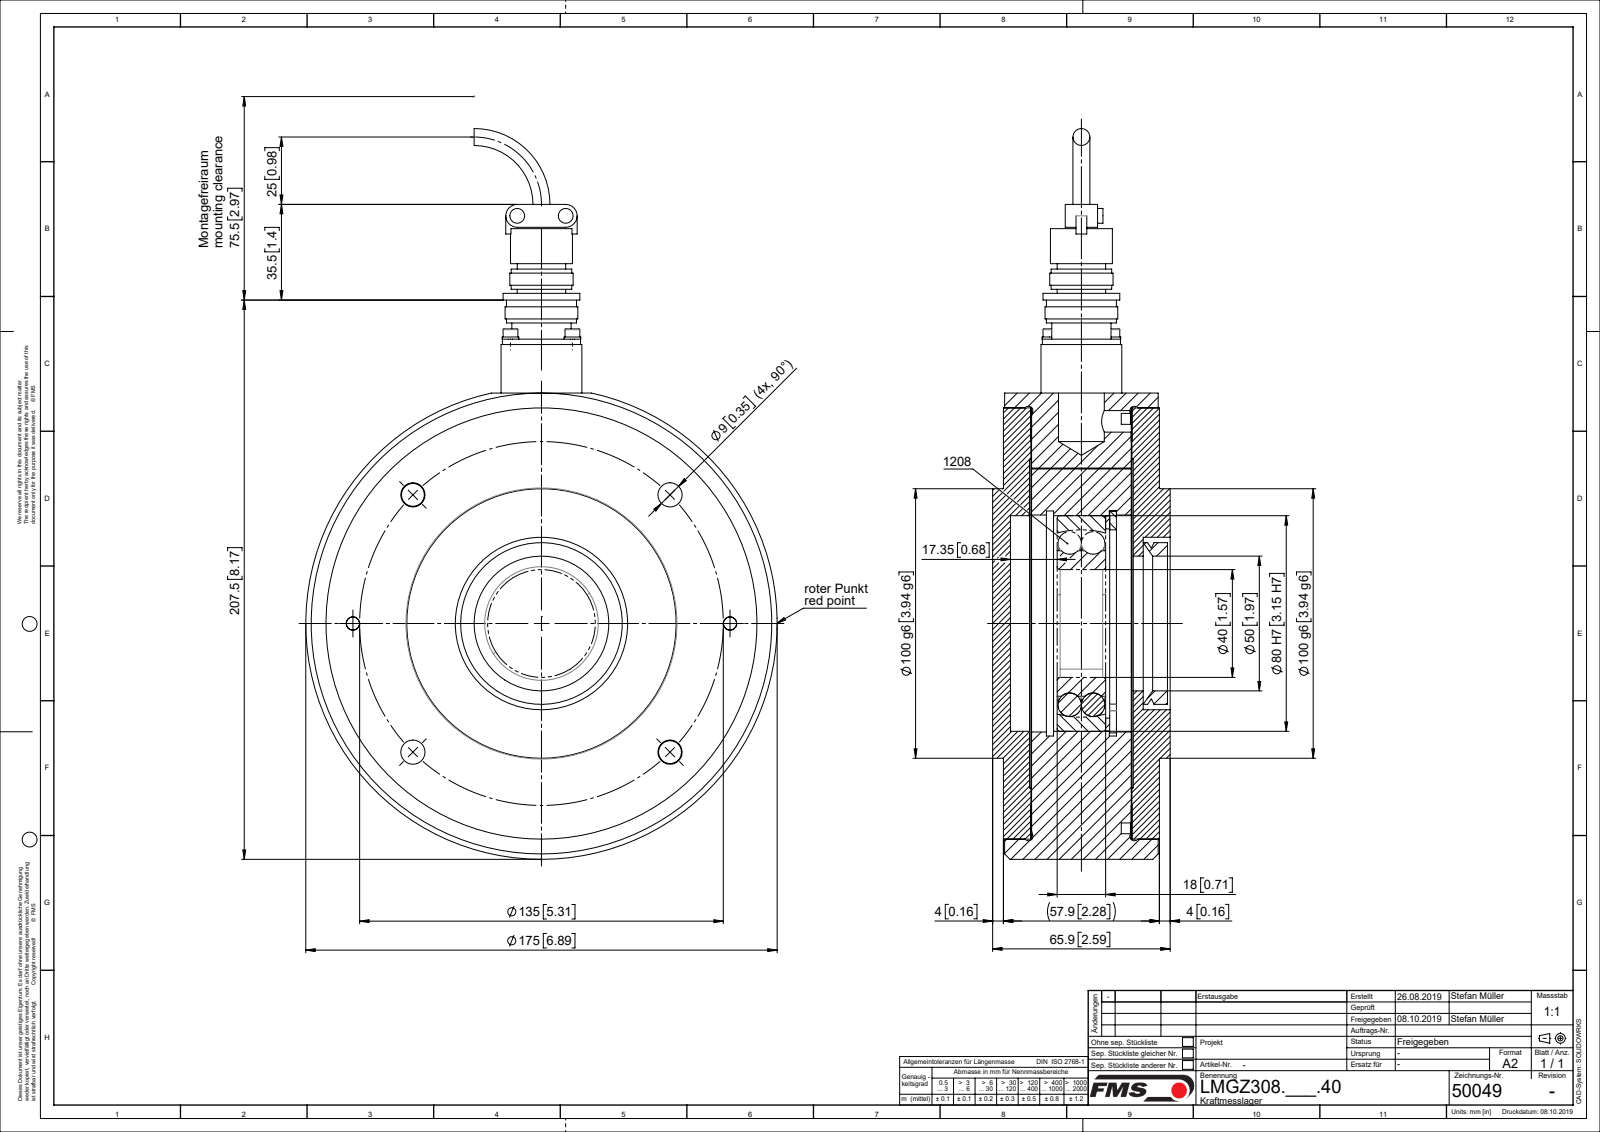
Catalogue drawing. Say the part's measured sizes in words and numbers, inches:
The part is named "L50049; L4857104; ~TEIL1; L49015 (+8 more)". Its 3-D file was written by "Mechanical Desktop 2007 (CONFIG_CONTROL_DESIGN)". It is 22 solids with 391 faces: 104 planar, 235 cylindrical and 52 other. Overall it measures 10.675 by 6.89 by 2.594 inches. Its volume is 77.44 cubic inches and its surface area 425.3 square inches. Round holes: 4 of diameter 0.102, 4 of diameter 0.126, 4 of diameter 0.134, 4 of diameter 0.354, 2 of diameter 0.203, 2 of diameter 0.26, 2 of diameter 0.342, 2 of diameter 0.433, 1 of diameter 0.906, 1 of diameter 1.575, 1 of diameter 1.89, 1 of diameter 1.969. Round bosses or shafts: 6 of diameter 0.217, 4 of diameter 0.244, 4 of diameter 0.118, 4 of diameter 0.098, 2 of diameter 0.394, 2 of diameter 0.236, 1 of diameter 6.89, 1 of diameter 6.299. Partial cylindrical surfaces (rounded edges, fillets, slot ends): 2 of radius 0.167, 2 of radius 0.295. The main face-to-face distances are 1.467, 0.402, 0.411, 1.868, 1.878, 1.457, 1.476, 0.02, 1.496, 0.382. The hole center spacings are 0.64, 0.906, 2.074, 2.657, 3.758, 5.002, 1.281, 2.756.
